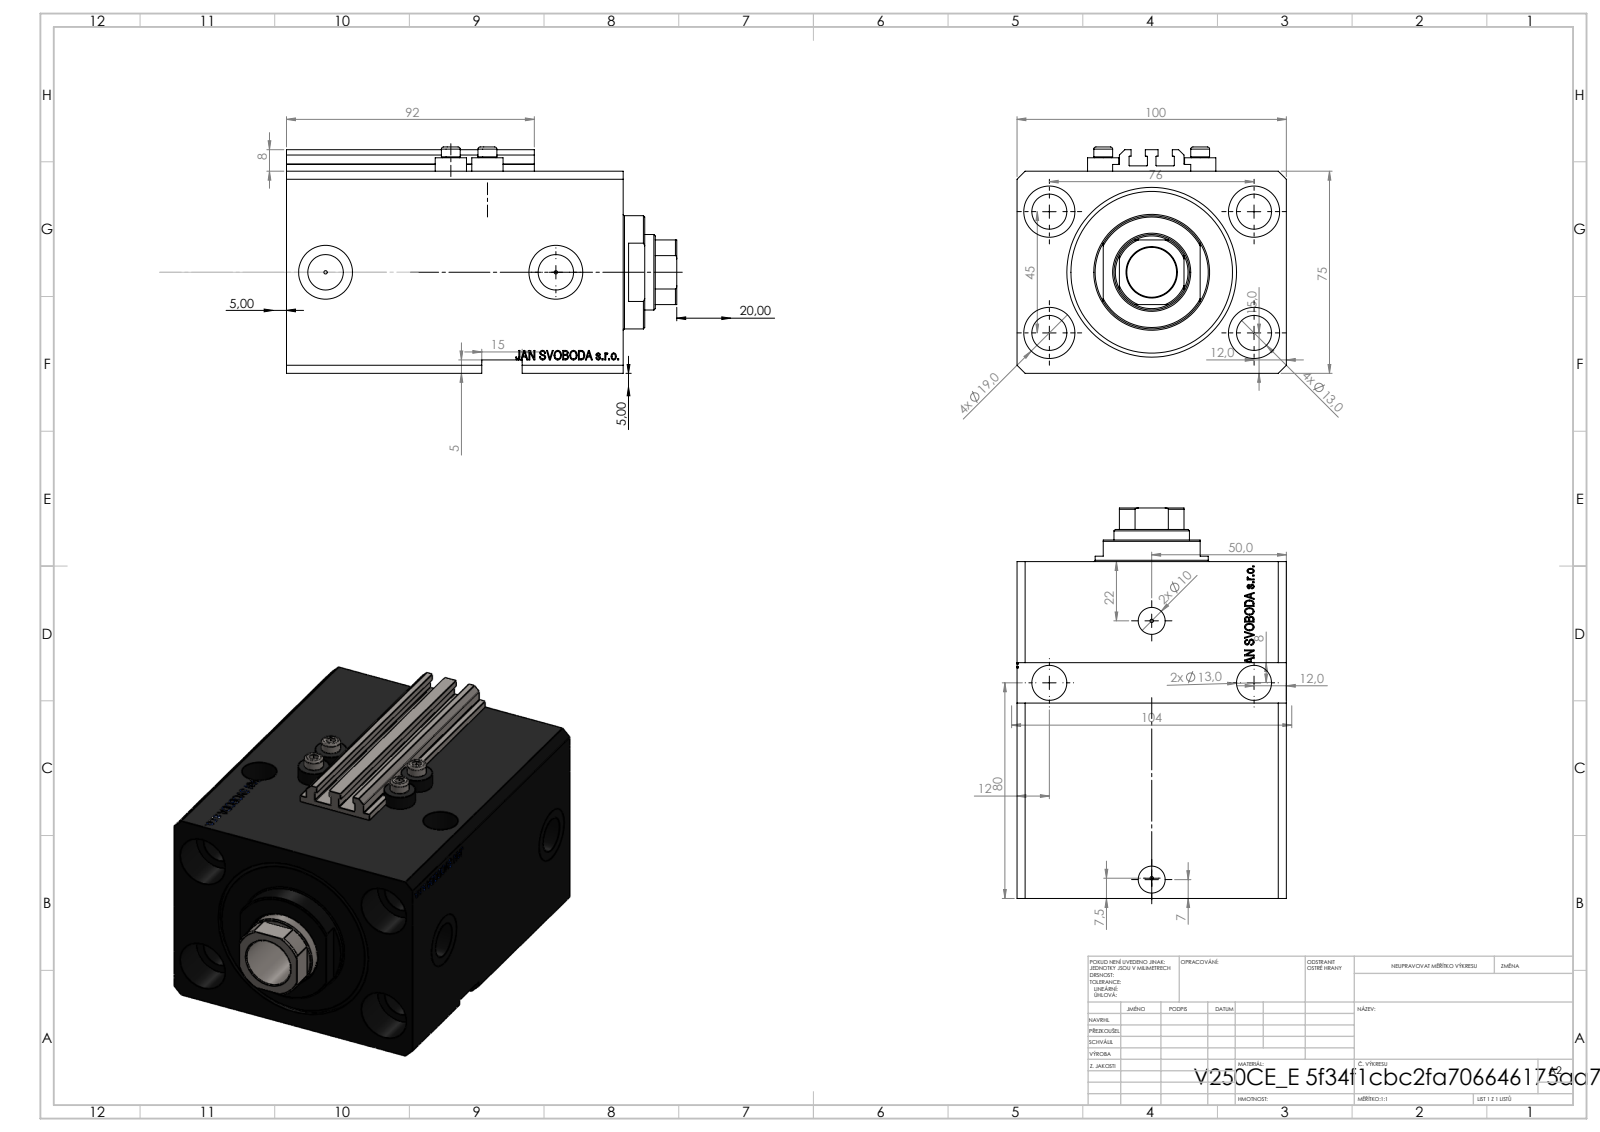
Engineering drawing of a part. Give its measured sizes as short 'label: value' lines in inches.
name: V250CE_VC_E; ALLEN BOLT V250CE; V250CE_E_Body; V250CE_C_VCP
written by: SolidWorks 2019 (CONFIG_CONTROL_DESIGN)
unit: in
bodies: 8 solids, 1124 faces (539 planar, 158 cylindrical, 427 other)
size: 5.709 × 3.937 × 3.307
volume: 46.69 in³; area: 234.9 in²
holes: 8× ⌀0.512, 4× ⌀0.049, 4× ⌀0.157, 4× ⌀0.748, 2× ⌀0.394, 2× ⌀0.518, 2× ⌀0.787, 1× ⌀0.728, 1× ⌀1.102, 1× ⌀1.969, 1× ⌀2.48
bosses: 4× ⌀0.457, 4× ⌀0.276, 1× ⌀1.654
rounds: 10× R0.008, 1× R0.531
face distances: 2.953, 3.937, 4.921, 0.787, 0.469, 4.453, 4.134, 3.665, 2.756, 0.512
hole spacings: 1.739, 2.992, 0.535, 0.816, 1.086, 1.142, 1.324, 1.417
